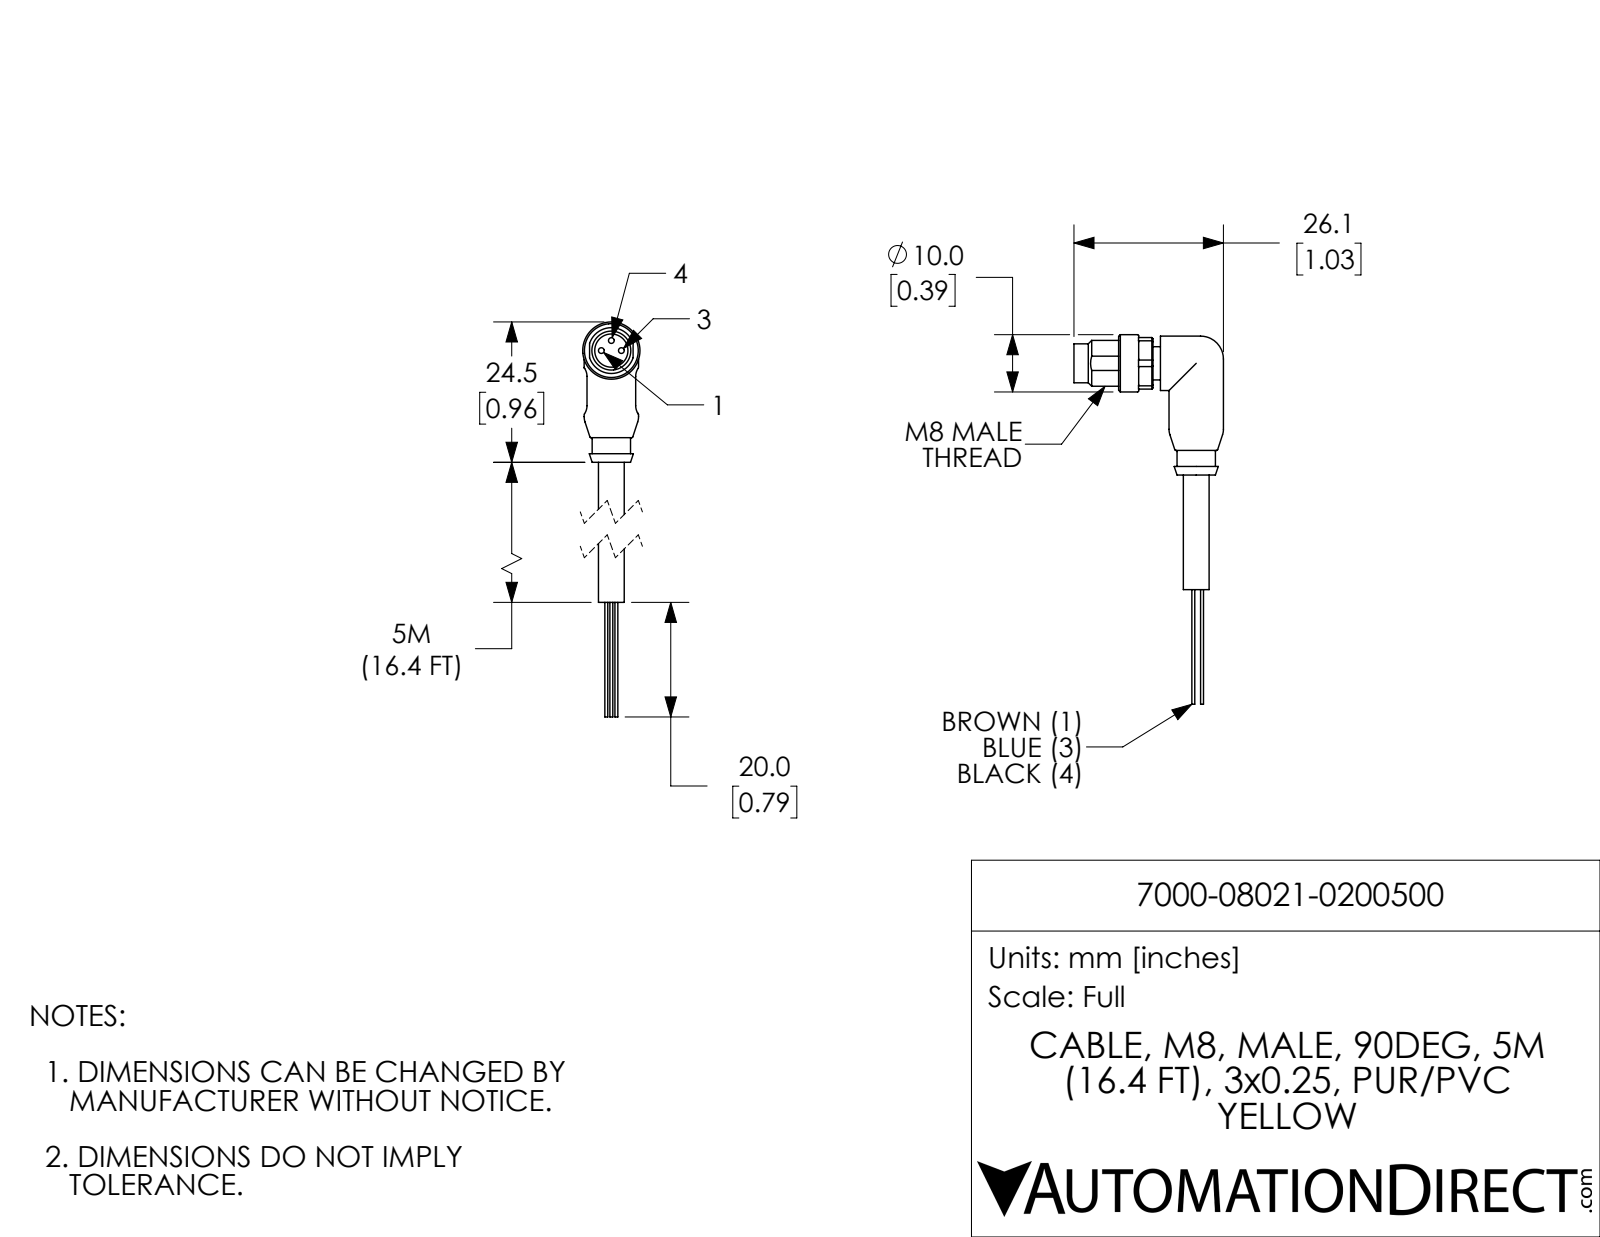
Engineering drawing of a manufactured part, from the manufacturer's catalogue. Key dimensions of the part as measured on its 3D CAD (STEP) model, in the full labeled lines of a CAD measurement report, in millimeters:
Part name (STEP PRODUCT): 7000-08021-0200500
STEP written by: SolidWorks 2017 (AUTOMOTIVE_DESIGN)
Units: millimetres
Bodies: 4 solids, 118 faces (40 planar, 45 cylindrical, 33 other)
Overall size (bounding box): 64.5 × 26.1 × 10
Volume: 2 640 mm³ · Surface area: 1 826 mm²
Round holes (diameter × count): ⌀5.8 ×1
Round bosses / shafts (diameter × count): ⌀1 ×3, ⌀0.5 ×3, ⌀9.5 ×2, ⌀10 ×1, ⌀8 ×1, ⌀6.8 ×1, ⌀6.7 ×1, ⌀4.5 ×1
Partial cylindrical surfaces — rounded edges, fillets, slot ends (radius × count): R0.2 ×4, R2.5 ×4, R4.9 ×1
Main face-to-face distances: 1.3, 9, 0.5, 8.1, 8.8, 10.1, 8.5, 2.8, 6, 7.3
